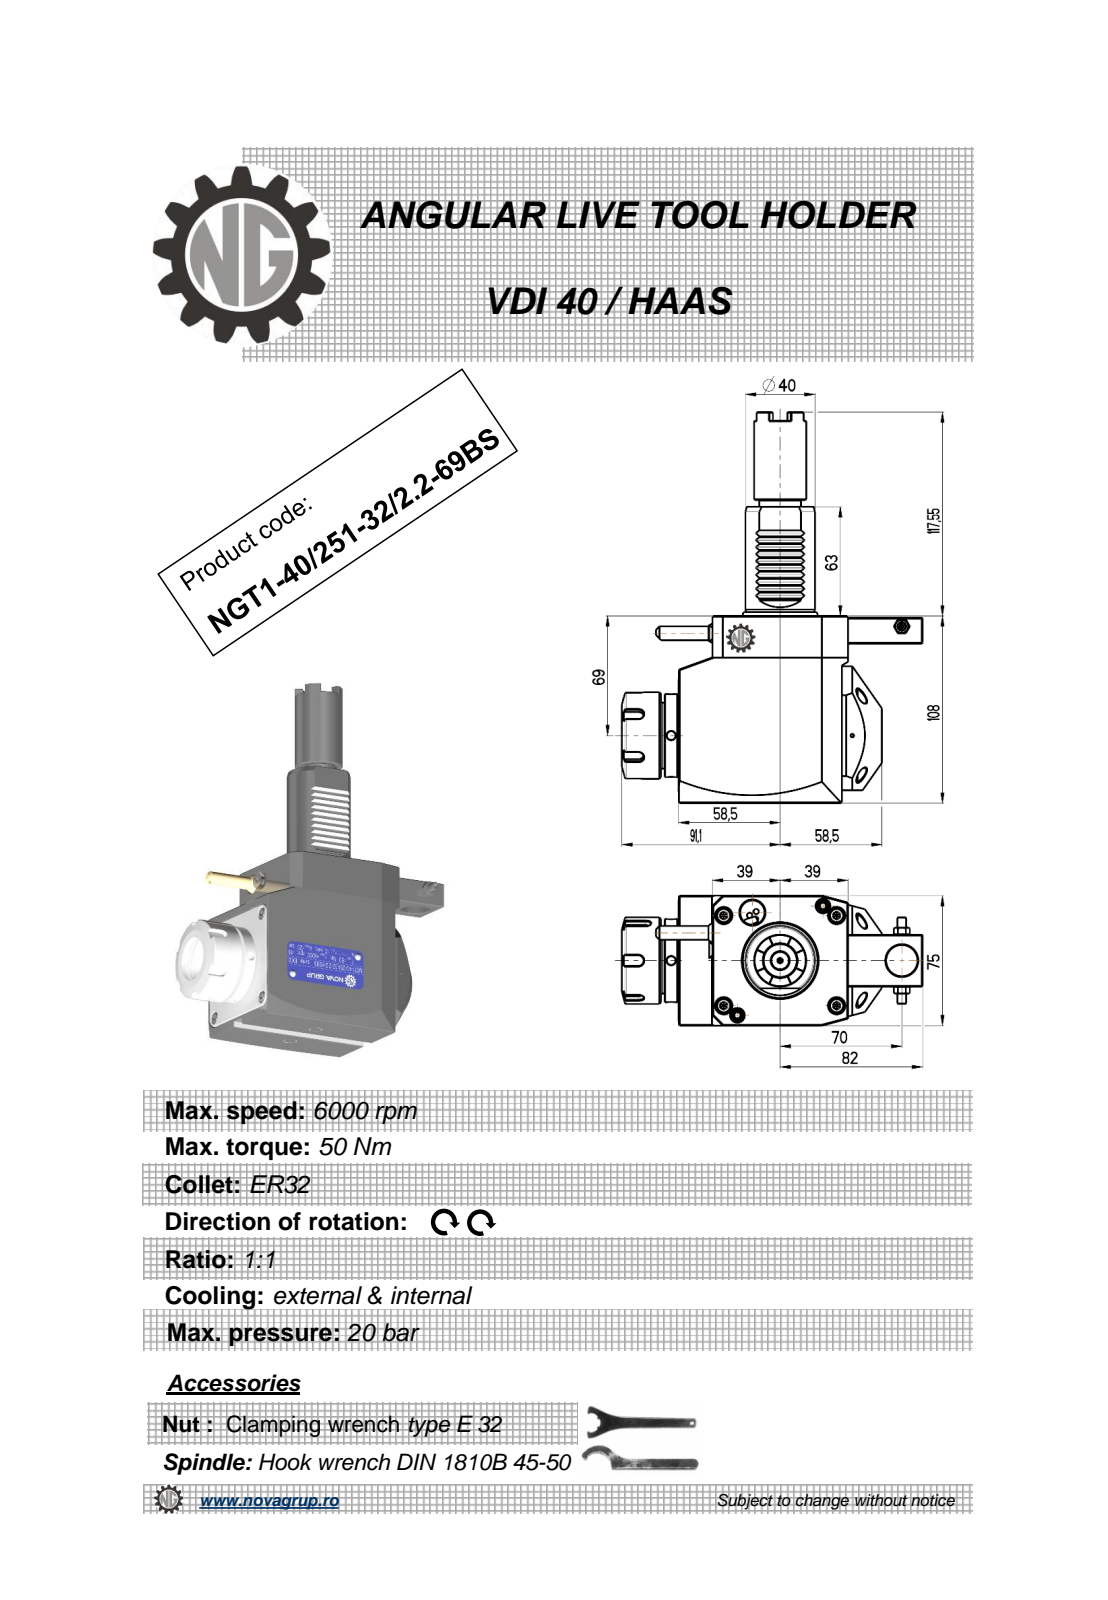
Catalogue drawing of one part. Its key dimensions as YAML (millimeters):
part_name: "NGT1_40_251_32_2_2_69BS"
step_written_by: "PRO/ENGINEER BY PARAMETRIC TECHNOLOGY CORPORATION, 2010280 (CONFIG_CONTROL_DESIGN)"
units: millimeters
bodies: {solids: 1, faces: 475, planar: 236, cylindrical: 100, other: 139}
overall_size: [225.55, 173.1, 76.6]
volume: 966789
surface_area: 79919
round_holes:
  - {diameter: 5, count: 3}
  - {diameter: 3, count: 1}
  - {diameter: 4.2, count: 1}
  - {diameter: 9.5, count: 1}
  - {diameter: 18, count: 1}
  - {diameter: 27, count: 1}
round_bosses_or_shafts:
  - {diameter: 50, count: 1}
  - {diameter: 48, count: 1}
  - {diameter: 41.5, count: 1}
  - {diameter: 41, count: 1}
  - {diameter: 40, count: 1}
  - {diameter: 30, count: 1}
  - {diameter: 24, count: 1}
  - {diameter: 10, count: 1}
partial_cylinders:
  - {radius: 0.26, count: 12}
  - {radius: 0.3, count: 10}
  - {radius: 0.2, count: 6}
  - {radius: 3, count: 5}
  - {radius: 5.8, count: 2}
  - {radius: 6, count: 2}
  - {radius: 600, count: 2}
  - {radius: 0.5, count: 1}
face_to_face_distances: [75, 108, 19.5, 97.5, 1, 3.5, 22.5, 78, 19.3, 97.3]
hole_center_spacings: [16.19, 61.13, 61.5, 132.75, 146.94]
